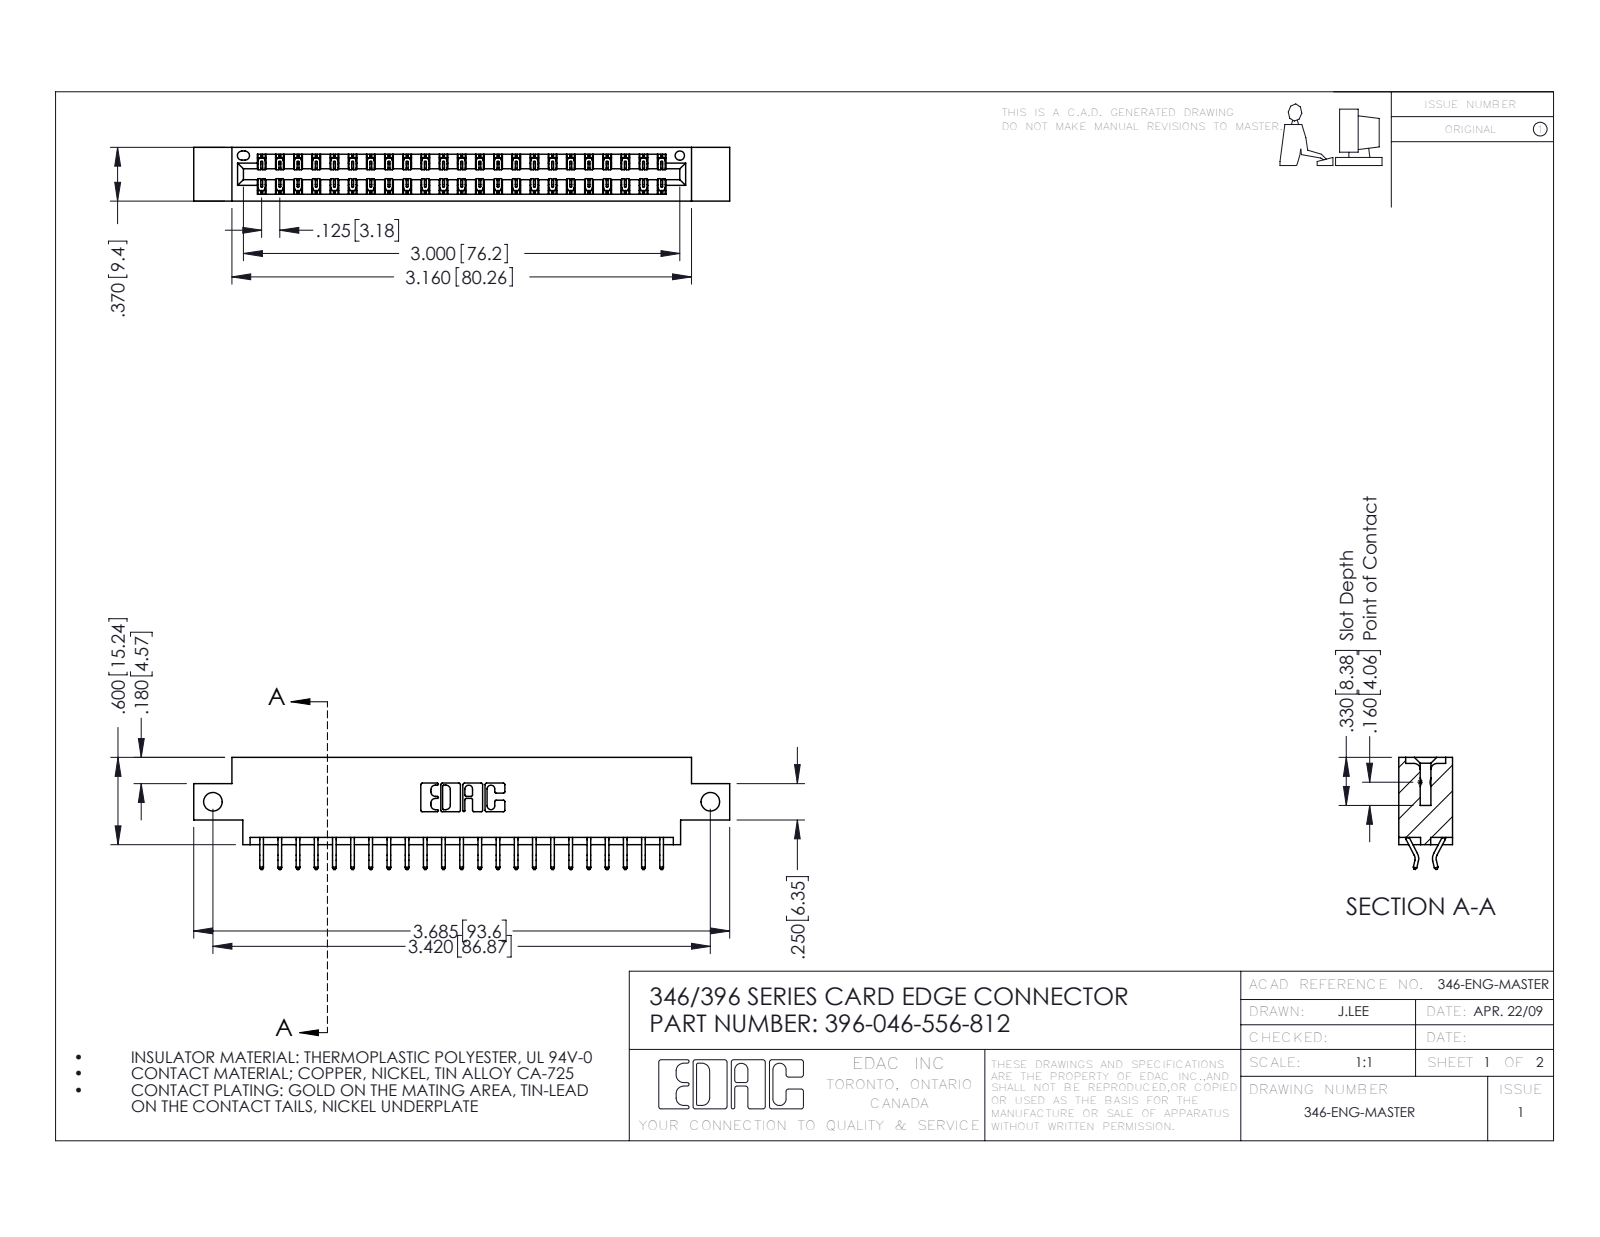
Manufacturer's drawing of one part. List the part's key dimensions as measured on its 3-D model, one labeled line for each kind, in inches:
Part name (STEP PRODUCT): 345-292-001_556 Tail; 396-046-556-812; 346 Part_0.170 Offset - Side Mount
STEP written by: SolidWorks 2016 (CONFIG_CONTROL_DESIGN)
Units: inches
Bodies: 47 solids, 2794 faces (1874 planar, 920 cylindrical, 0 other)
Overall size (bounding box): 3.685 × 0.77 × 0.37
Volume: 0.533 in³ · Surface area: 18.15 in²
Round holes (diameter × count): ⌀0.128 ×2, ⌀0.064 ×1
Partial cylindrical surfaces — rounded edges, fillets, slot ends (radius × count): R0.006 ×69, R0.01 ×22, R0.007 ×6, R0.031 ×6, R0.026 ×3, R0.01 ×2, R0.014 ×2, R0.022 ×2
Main face-to-face distances: 0.048, 0.322, 0.37, 0.25, 0.025, 0.072, 0.298, 0.275, 0.148, 0.222
Hole centre spacings: 3.42
